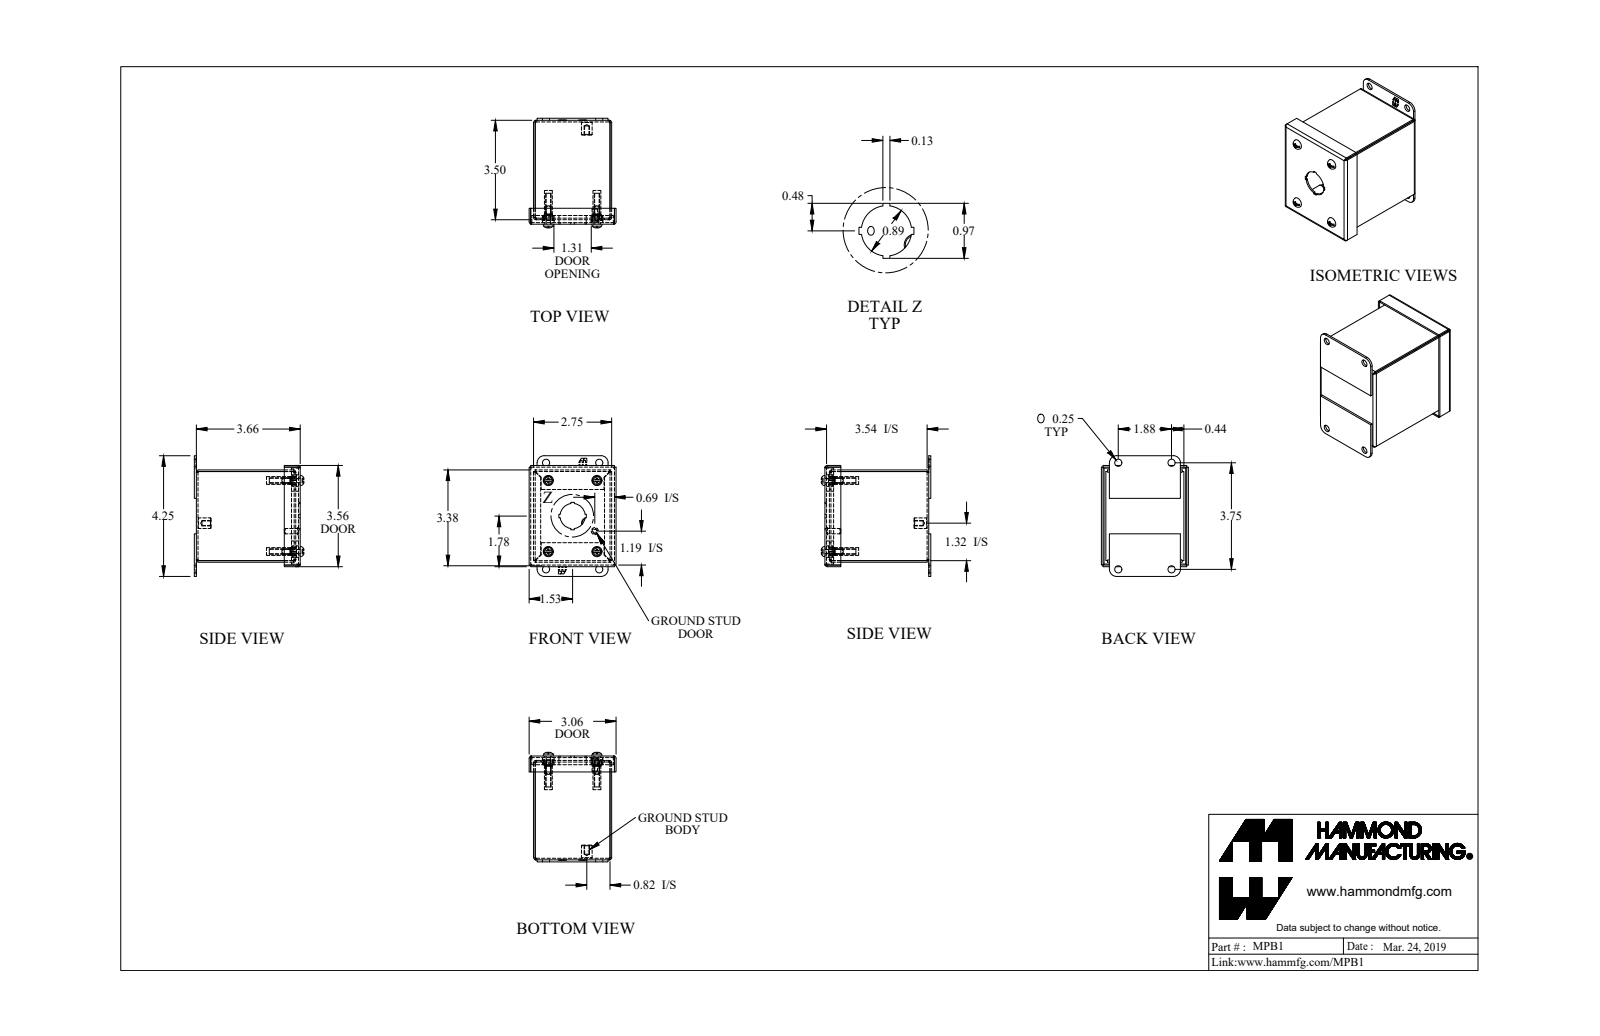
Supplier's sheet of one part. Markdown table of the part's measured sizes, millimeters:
| quantity | value |
| --- | --- |
| part name | MPB1 |
| STEP written by | SolidWorks 2018 (AUTOMOTIVE_DESIGN) |
| units | millimeters |
| bodies | 19 solids, 571 faces (371 planar, 144 cylindrical, 56 other) |
| overall size | 108 × 97.9 × 77.8 |
| volume | 96 190 mm³ |
| surface area | 118 100 mm² |
| round holes (diameter × count) | 6.4 × 8, 4 × 4, 10.3 × 4, 4 × 1, 22.5 × 1 |
| round bosses / shafts (diameter × count) | 9.9 × 4, 4.8 × 4, 3.8 × 4, 7 × 2, 7 × 2, 9.5 × 1, 6.4 × 1, 4.8 × 1 |
| partial cylindrical surfaces (radius × count) | 0.7 × 12, 2.2 × 12, 4.1 × 4, 4.3 × 4, 6.4 × 4 |
| main face-to-face distances | 1.4, 1.4, 91.4, 68.4, 81.1, 69.9, 67, 4, 92.9, 79.7 |
| hole center spacings | 48.2, 43.5, 16, 63.5, 79.4, 91.5, 38.5, 43.4 |
